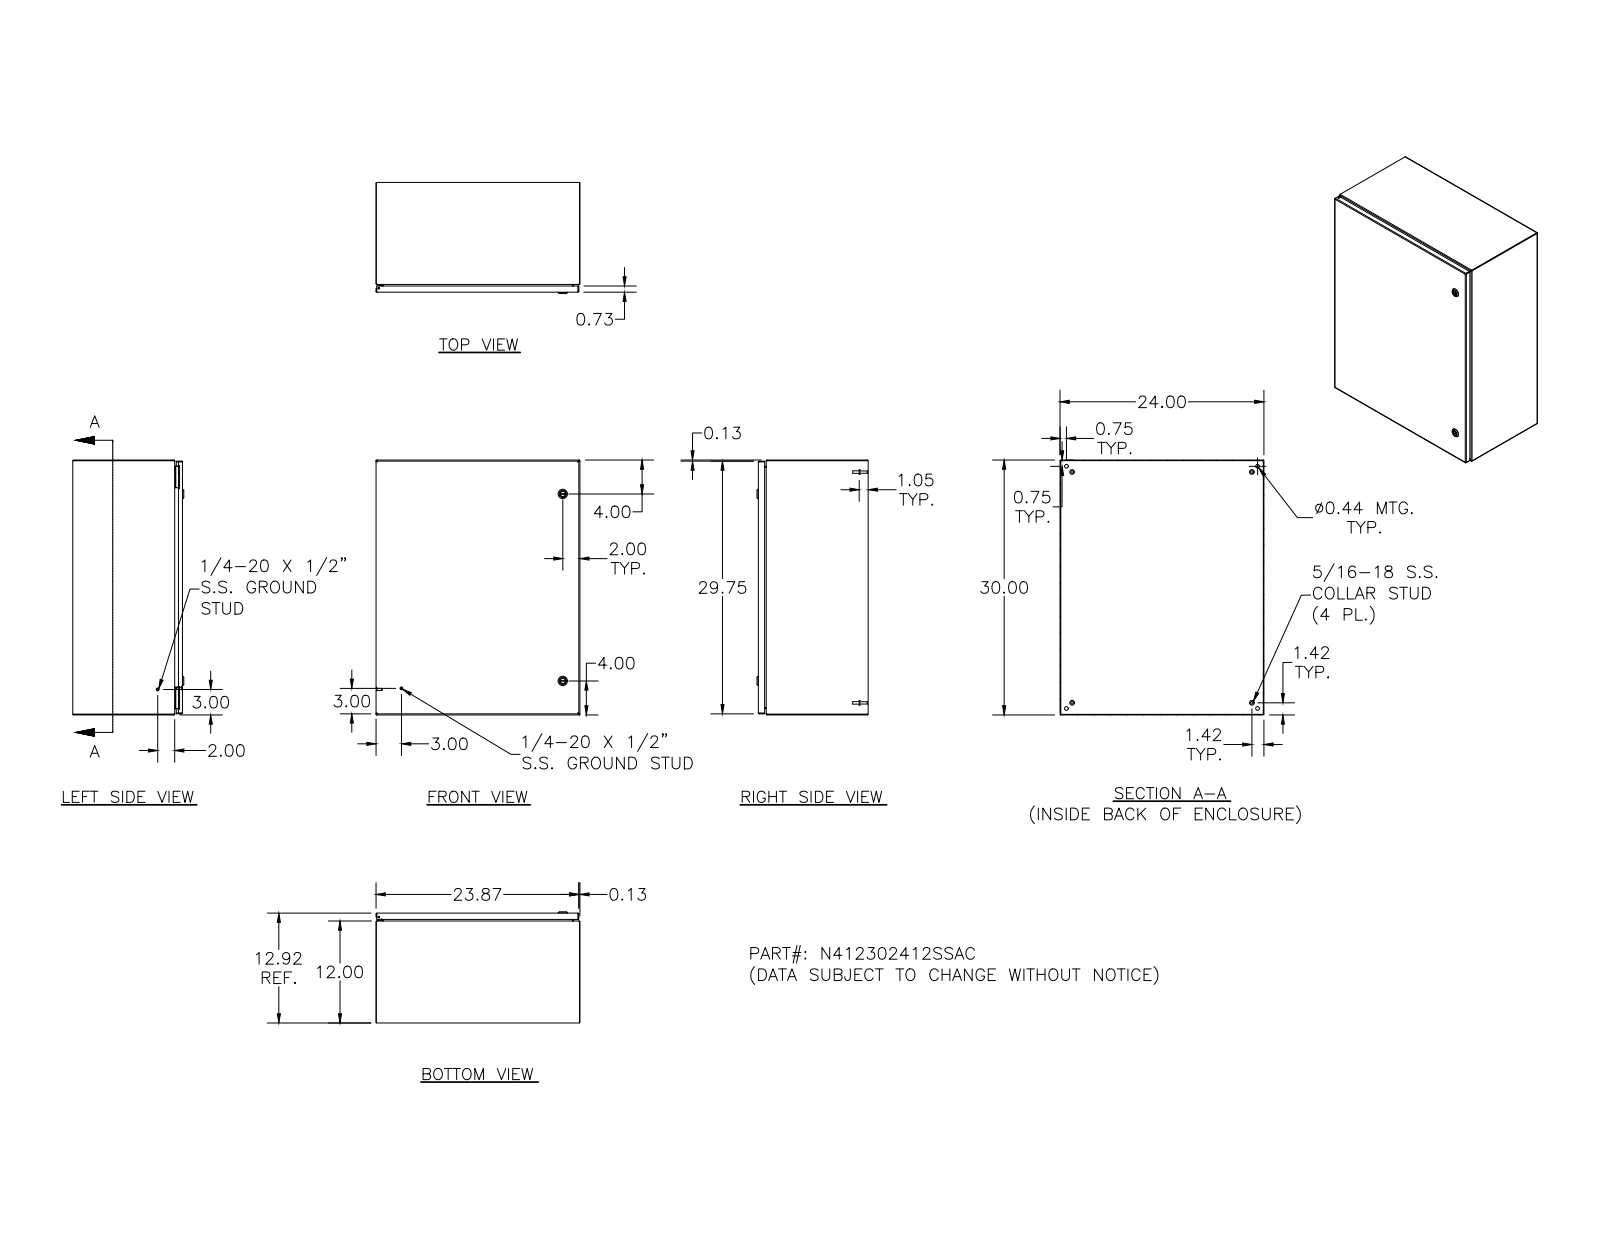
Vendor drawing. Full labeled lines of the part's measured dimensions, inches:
Part name (STEP PRODUCT): N412302412SSAC; N412302412SSACBKP; 388151; N4123024SSACLID (+8 more)
STEP written by: Autodesk Inventor 2011 (AUTOMOTIVE_DESIGN)
Units: inches
Bodies: 42 solids, 1662 faces (698 planar, 588 cylindrical, 376 other)
Overall size (bounding box): 30 × 24 × 13.075
Volume: 218.9 in³ · Surface area: 5 937 in²
Round holes (diameter × count): ⌀0.188 ×5, ⌀0.093 ×4, ⌀0.152 ×4, ⌀0.167 ×4, ⌀0.172 ×4, ⌀0.437 ×4, ⌀0.156 ×2, ⌀0.197 ×2, ⌀0.315 ×2, ⌀0.394 ×2, ⌀0.402 ×2, ⌀0.634 ×2
Round bosses / shafts (diameter × count): ⌀0.25 ×10, ⌀0.563 ×4, ⌀0.36 ×4, ⌀0.32 ×4, ⌀0.3 ×4, ⌀0.275 ×4, ⌀0.256 ×4, ⌀0.164 ×4
Partial cylindrical surfaces — rounded edges, fillets, slot ends (radius × count): R0.05 ×26, R0.016 ×18, R0.016 ×16, R0.09 ×16, R0.02 ×15, R0.031 ×14, R0.125 ×14, R0.032 ×8
Main face-to-face distances: 0.074, 12.843, 23.926, 12.917, 12.769, 29.926, 24, 23.852, 30, 29.852
Hole centre spacings: 26, 0.017, 0.66, 22.869, 0.019, 0.5, 0.648, 0.652
